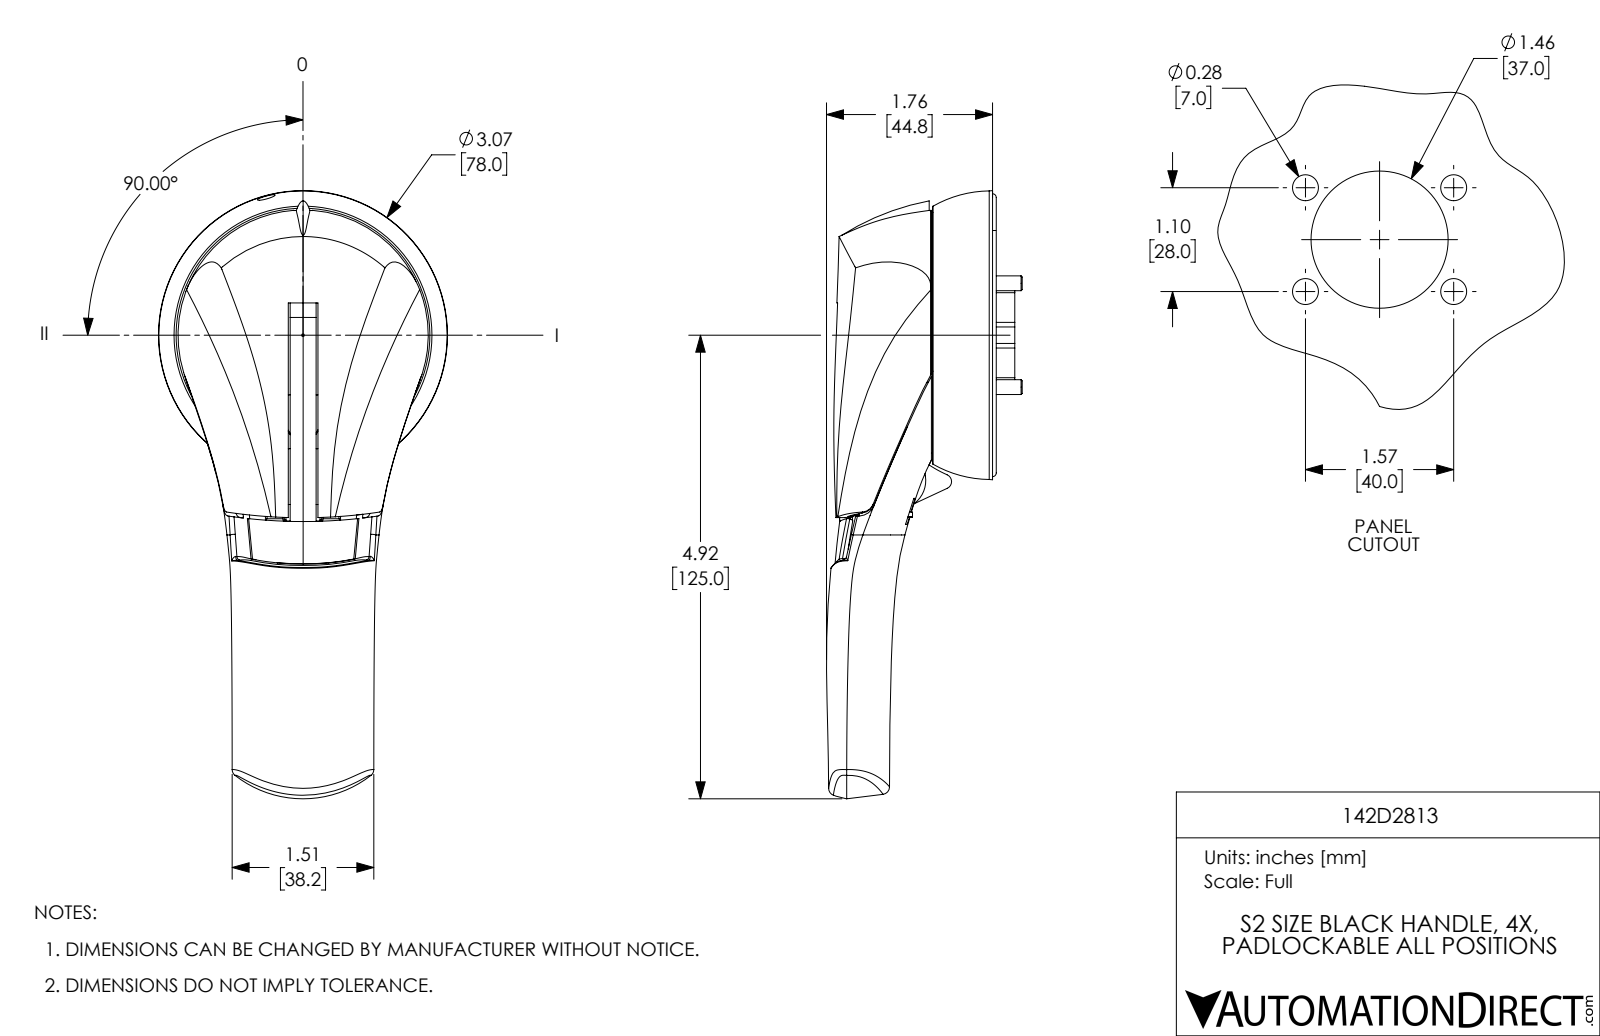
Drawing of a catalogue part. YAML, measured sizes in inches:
part_name: "142D2813"
step_written_by: "SolidWorks 2017 (AUTOMOTIVE_DESIGN)"
units: inches
bodies: {solids: 8, faces: 1516, planar: 810, cylindrical: 548, other: 158}
overall_size: [6.458, 3.07, 2.079]
volume: 9.514
surface_area: 87.31
round_holes:
  - {diameter: 0.157, count: 6}
  - {diameter: 0.339, count: 4}
  - {diameter: 0.425, count: 4}
  - {diameter: 0.03, count: 3}
  - {diameter: 0.169, count: 2}
  - {diameter: 0.362, count: 2}
  - {diameter: 0.118, count: 1}
  - {diameter: 0.189, count: 1}
  - {diameter: 2.992, count: 1}
round_bosses_or_shafts:
  - {diameter: 0.02, count: 11}
  - {diameter: 0.335, count: 4}
  - {diameter: 0.315, count: 4}
  - {diameter: 0.089, count: 3}
  - {diameter: 0.069, count: 3}
  - {diameter: 0.228, count: 2}
  - {diameter: 2.819, count: 1}
  - {diameter: 2.701, count: 1}
partial_cylinders:
  - {radius: 0.01, count: 221}
  - {radius: 0.015, count: 20}
  - {radius: 0.034, count: 20}
  - {radius: 0.03, count: 15}
  - {radius: 0.039, count: 4}
  - {radius: 0.025, count: 3}
  - {radius: 5.437, count: 3}
  - {radius: 0.079, count: 2}
face_to_face_distances: [0.024, 0.701, 0.713, 0.689, 0.035, 0.102, 0.276, 0.173, 0.244, 0.047]
hole_center_spacings: [0.961, 0.309, 0.669, 1.098, 1.102, 1.203, 1.575, 1.881]
